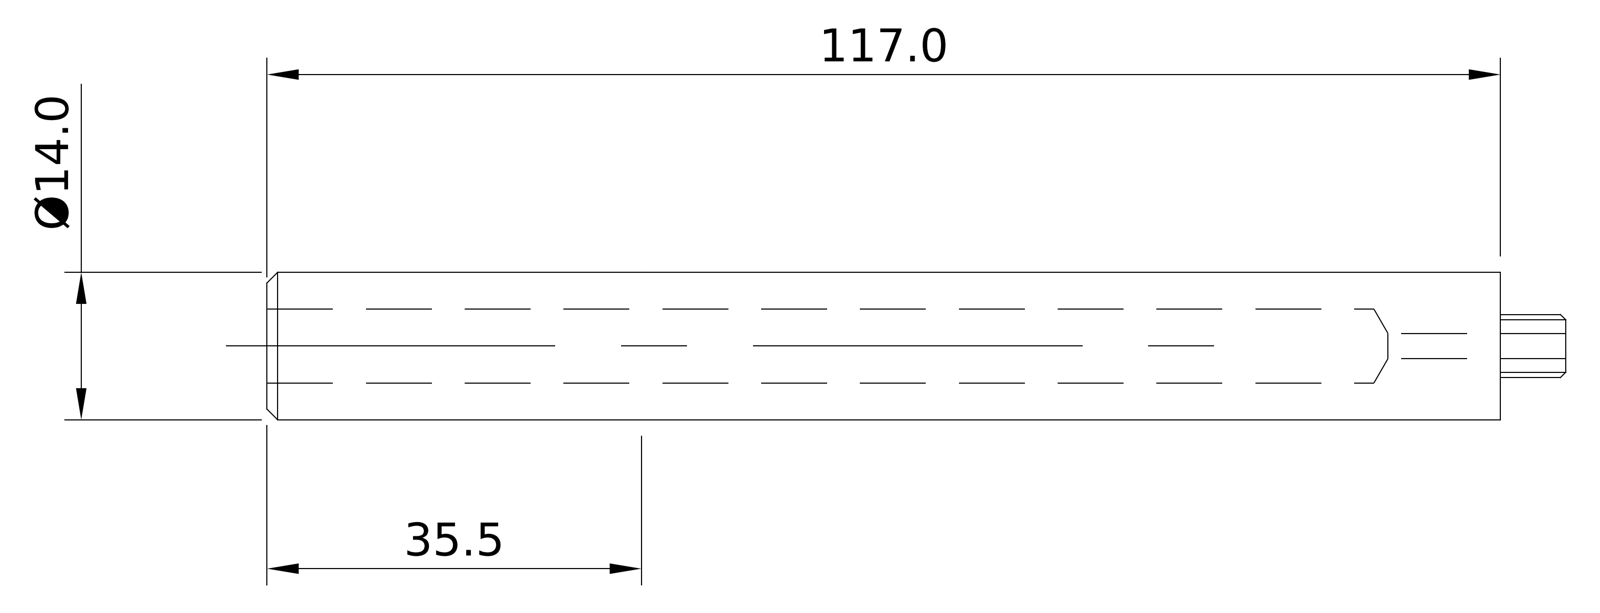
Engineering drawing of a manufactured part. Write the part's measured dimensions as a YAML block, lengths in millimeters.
step_written_by: "ACIS (automotive_design)"
units: millimeters
bodies: {solids: 1, faces: 19, planar: 3, cylindrical: 8, other: 8}
overall_size: [123, 14, 14]
volume: 16699
surface_area: 7020
round_holes:
  - {diameter: 2.2, count: 1}
  - {diameter: 4, count: 1}
round_bosses_or_shafts:
  - {diameter: 14, count: 1}
  - {diameter: 6, count: 1}
face_to_face_distances: [117, 6, 123]
